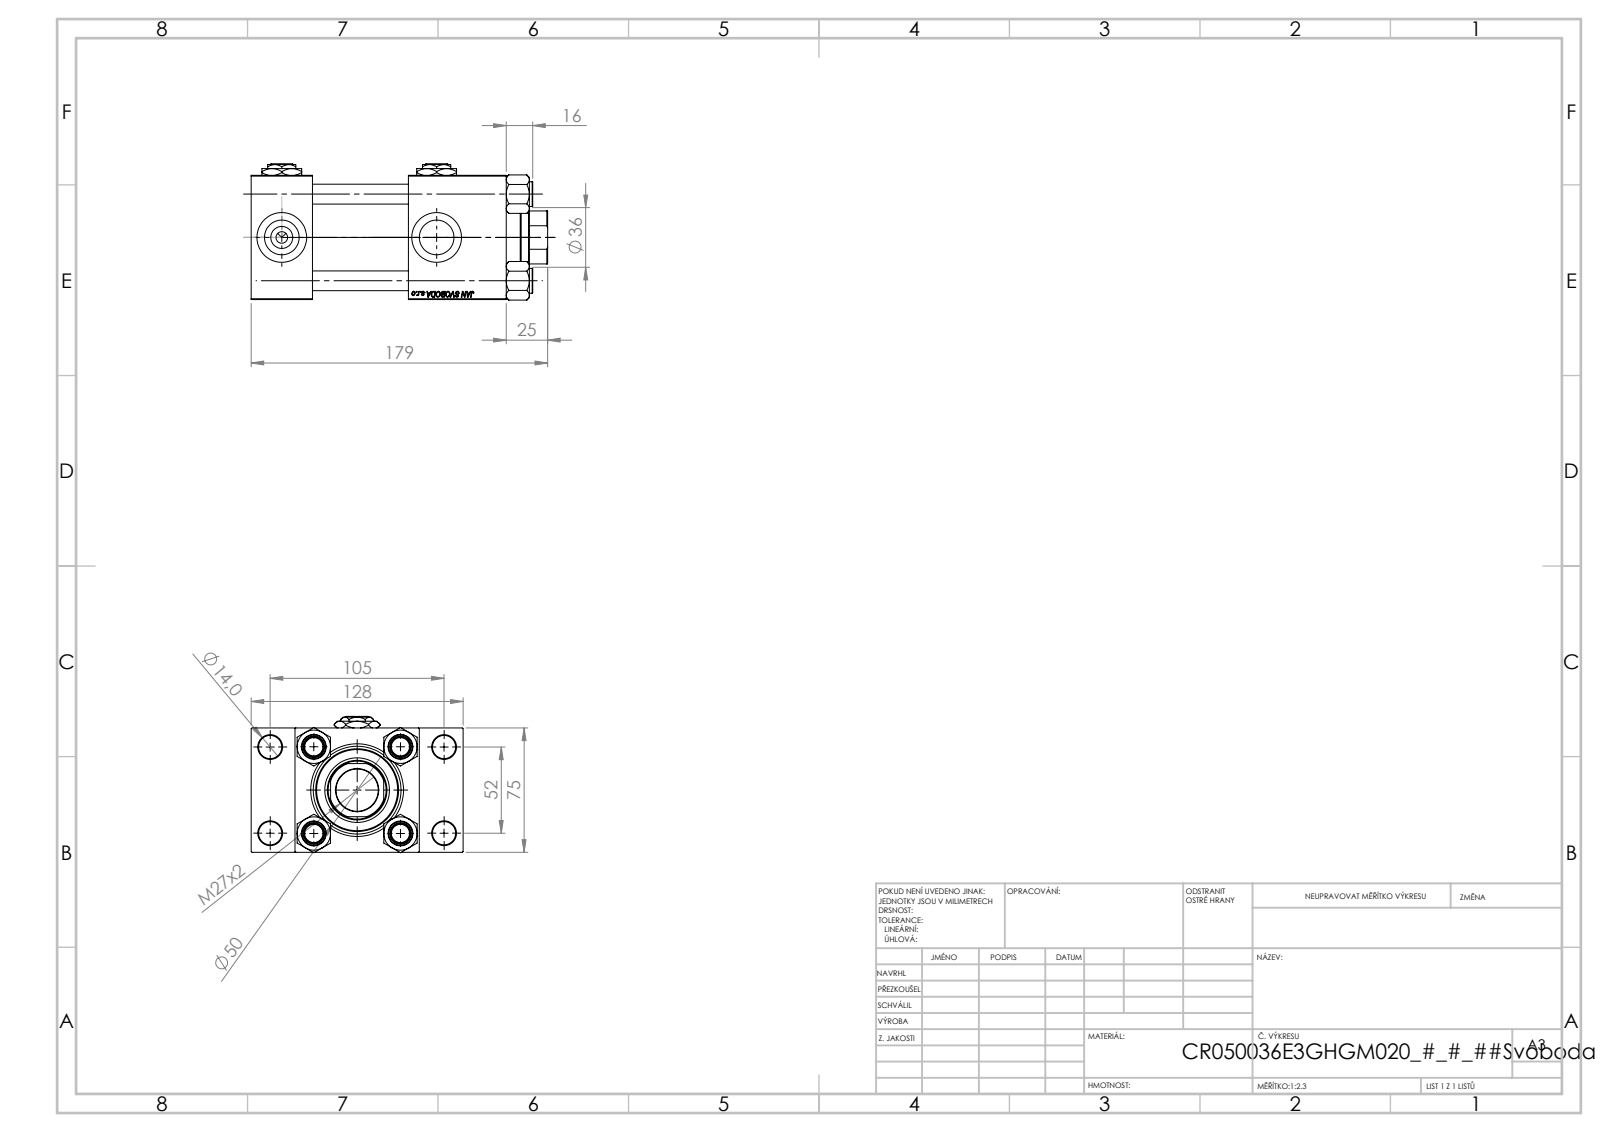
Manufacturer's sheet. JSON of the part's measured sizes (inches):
{"part_name": "V215_VC_A; Zatka_pro_OIL_PORT; V215CR_VCP_E; NUT_M5_E (+2 more)", "step_written_by": "SolidWorks 2019 (CONFIG_CONTROL_DESIGN)", "units": "inches", "bodies": {"solids": 13, "faces": 1236, "planar": 545, "cylindrical": 97, "other": 594}, "overall_size": [7.047, 5.039, 3.239], "volume_in3": 49.54, "surface_area_in2": 288, "round_holes": [[0.472, 4], [0.551, 4], [0.825, 4], [1.181, 4], [0.276, 3], [1.004, 1], [1.417, 1], [1.535, 1], [1.614, 1], [2.087, 1]], "round_bosses_or_shafts": [[0.591, 4], [2.205, 1], [1.969, 1]], "partial_cylinders_radius": [[0.689, 1]], "face_to_face_distances": [2.953, 1.457, 1.043, 3.996, 3.74, 4.606, 6.063, 2.323, 2.283, 4.933], "hole_center_spacings": [1.037, 1.456, 2.059, 2.3, 2.307, 3.096, 3.715, 2.047]}
